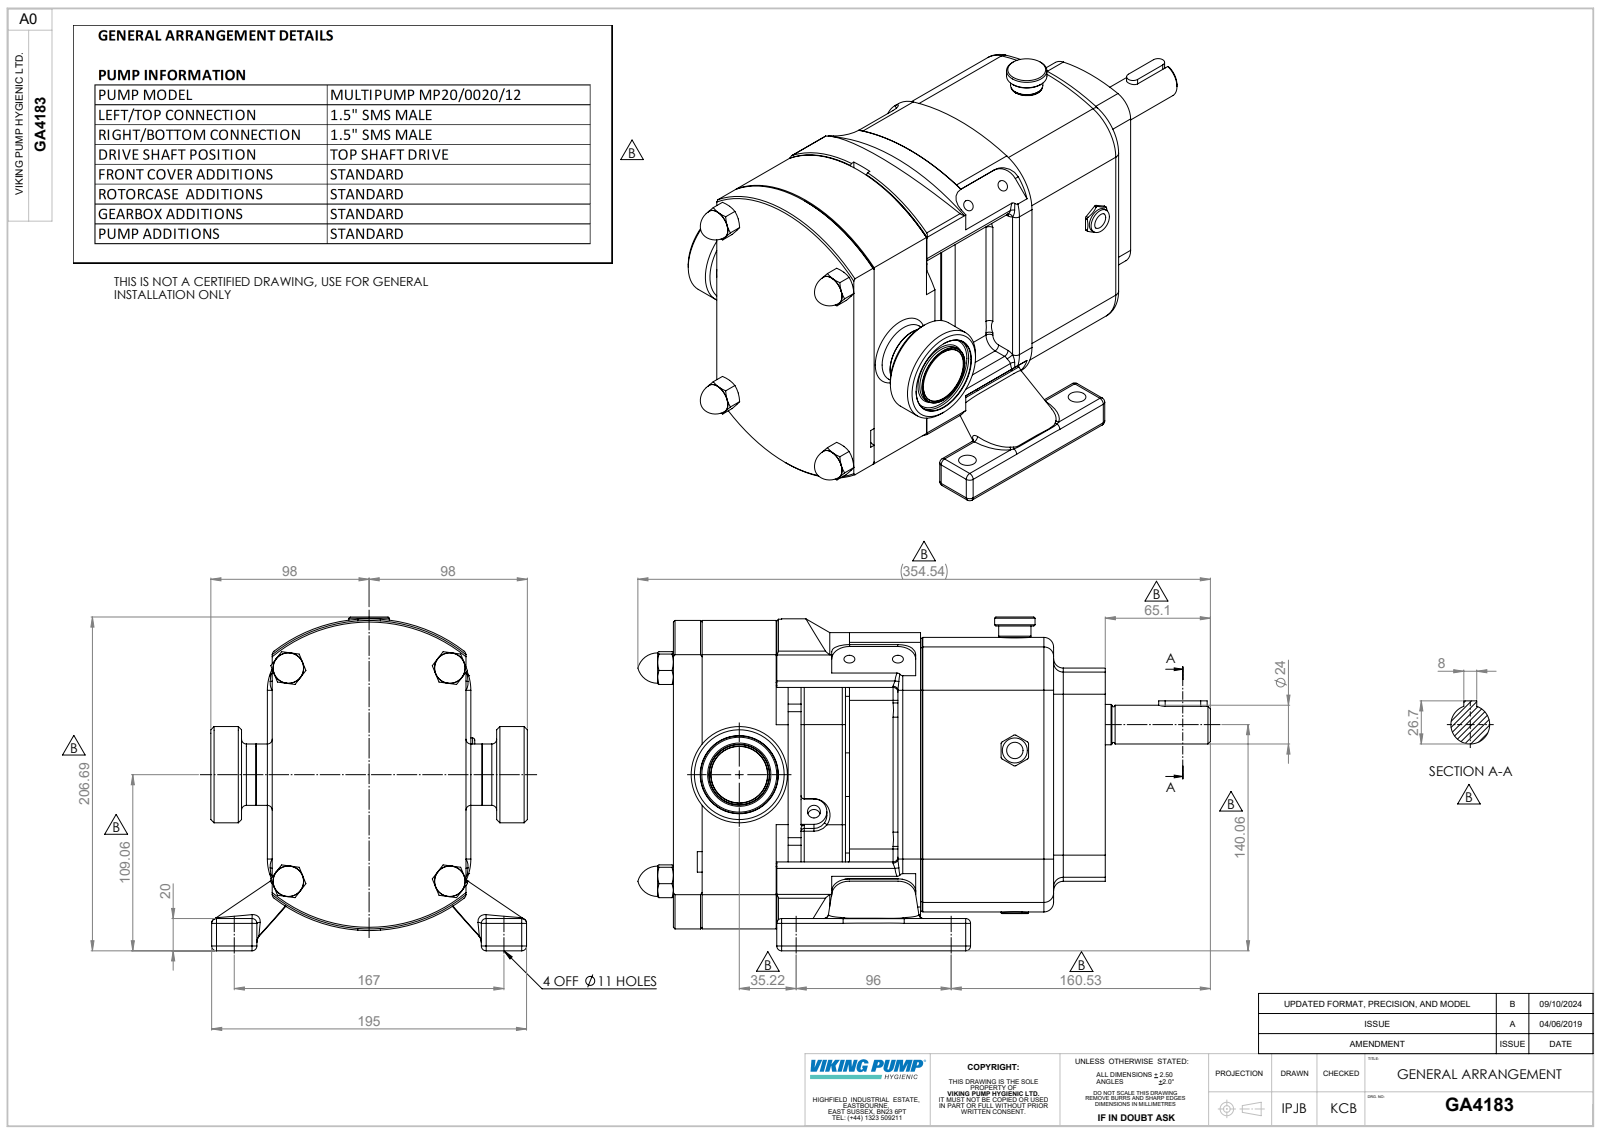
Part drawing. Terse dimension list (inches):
name: Copy (2) of CP20-0020-12 H T^GA4183; Copy of Z94-5101-22 - 1.5 INCH SMS681^GA4183; GA4183
written by: SolidWorks 2023 (AUTOMOTIVE_DESIGN)
unit: in
bodies: 3 solids, 847 faces (257 planar, 292 cylindrical, 298 other)
size: 13.958 × 8.137 × 7.717
volume: 293.5 in³; area: 471.4 in²
holes: 4× ⌀0.268, 4× ⌀0.433, 3× ⌀0.255, 2× ⌀0.315, 1× ⌀0.887, 1× ⌀1.378, 1× ⌀1.89
bosses: 2× ⌀1.378, 2× ⌀0.669, 1× ⌀2.346, 1× ⌀1.496, 1× ⌀1.48, 1× ⌀0.985, 1× ⌀0.984, 1× ⌀0.945
rounds: 55× R0.118, 18× R0.079, 16× R0.039, 8× R0.236, 8× R0.437, 6× R0.05, 6× R0.157, 6× R0.315
face distances: 4.724, 4.293, 6.236, 10.529, 0.984, 3.74, 0.798, 3.926, 0.186, 2.942
hole spacings: 2.114, 1.183, 3.636, 3.78, 6.576, 2.405, 6.264, 6.264
